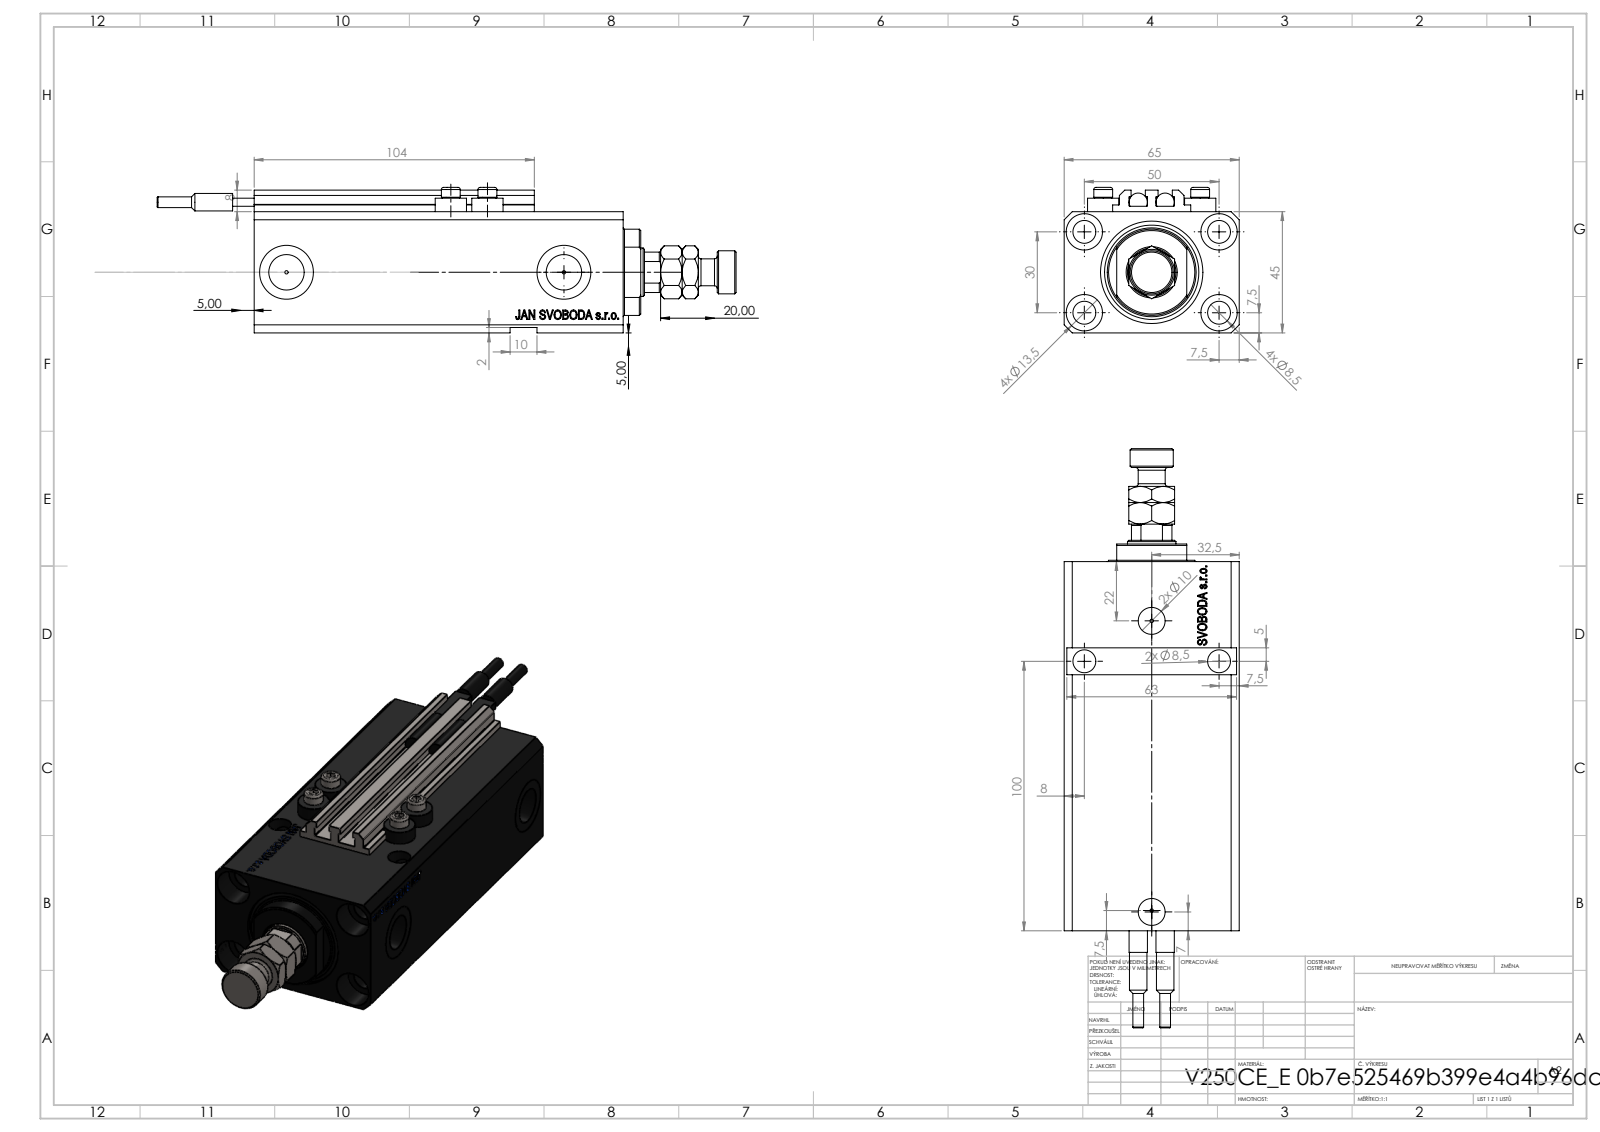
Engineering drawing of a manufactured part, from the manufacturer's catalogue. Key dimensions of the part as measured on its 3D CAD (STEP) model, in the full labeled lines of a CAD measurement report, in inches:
Part name (STEP PRODUCT): V250CE_VC_E; ALLEN BOLT V250CE; SWITCH_V250CE; V250CE_C_VCP (+2 more)
STEP written by: SolidWorks 2019 (CONFIG_CONTROL_DESIGN)
Units: inches
Bodies: 11 solids, 1207 faces (563 planar, 174 cylindrical, 470 other)
Overall size (bounding box): 8.465 × 2.559 × 2.126
Volume: 21.72 in³ · Surface area: 154.2 in²
Round holes (diameter × count): ⌀0.335 ×9, ⌀0.049 ×4, ⌀0.157 ×4, ⌀0.531 ×4, ⌀0.394 ×2, ⌀0.518 ×2, ⌀0.787 ×2, ⌀0.709 ×1, ⌀0.984 ×1, ⌀1.496 ×1
Round bosses / shafts (diameter × count): ⌀0.457 ×4, ⌀0.276 ×4, ⌀0.268 ×2, ⌀0.256 ×2, ⌀0.157 ×2, ⌀0.63 ×1, ⌀0.394 ×1
Partial cylindrical surfaces — rounded edges, fillets, slot ends (radius × count): R0.008 ×10, R0.335 ×1, R0.63 ×1
Main face-to-face distances: 1.772, 2.559, 1.85, 0.079, 0.551, 0.098, 0.394, 0.118, 4.843, 0.945
Hole centre spacings: 1.148, 1.969, 0.535, 0.595, 1.098, 1.181, 1.323, 1.324
